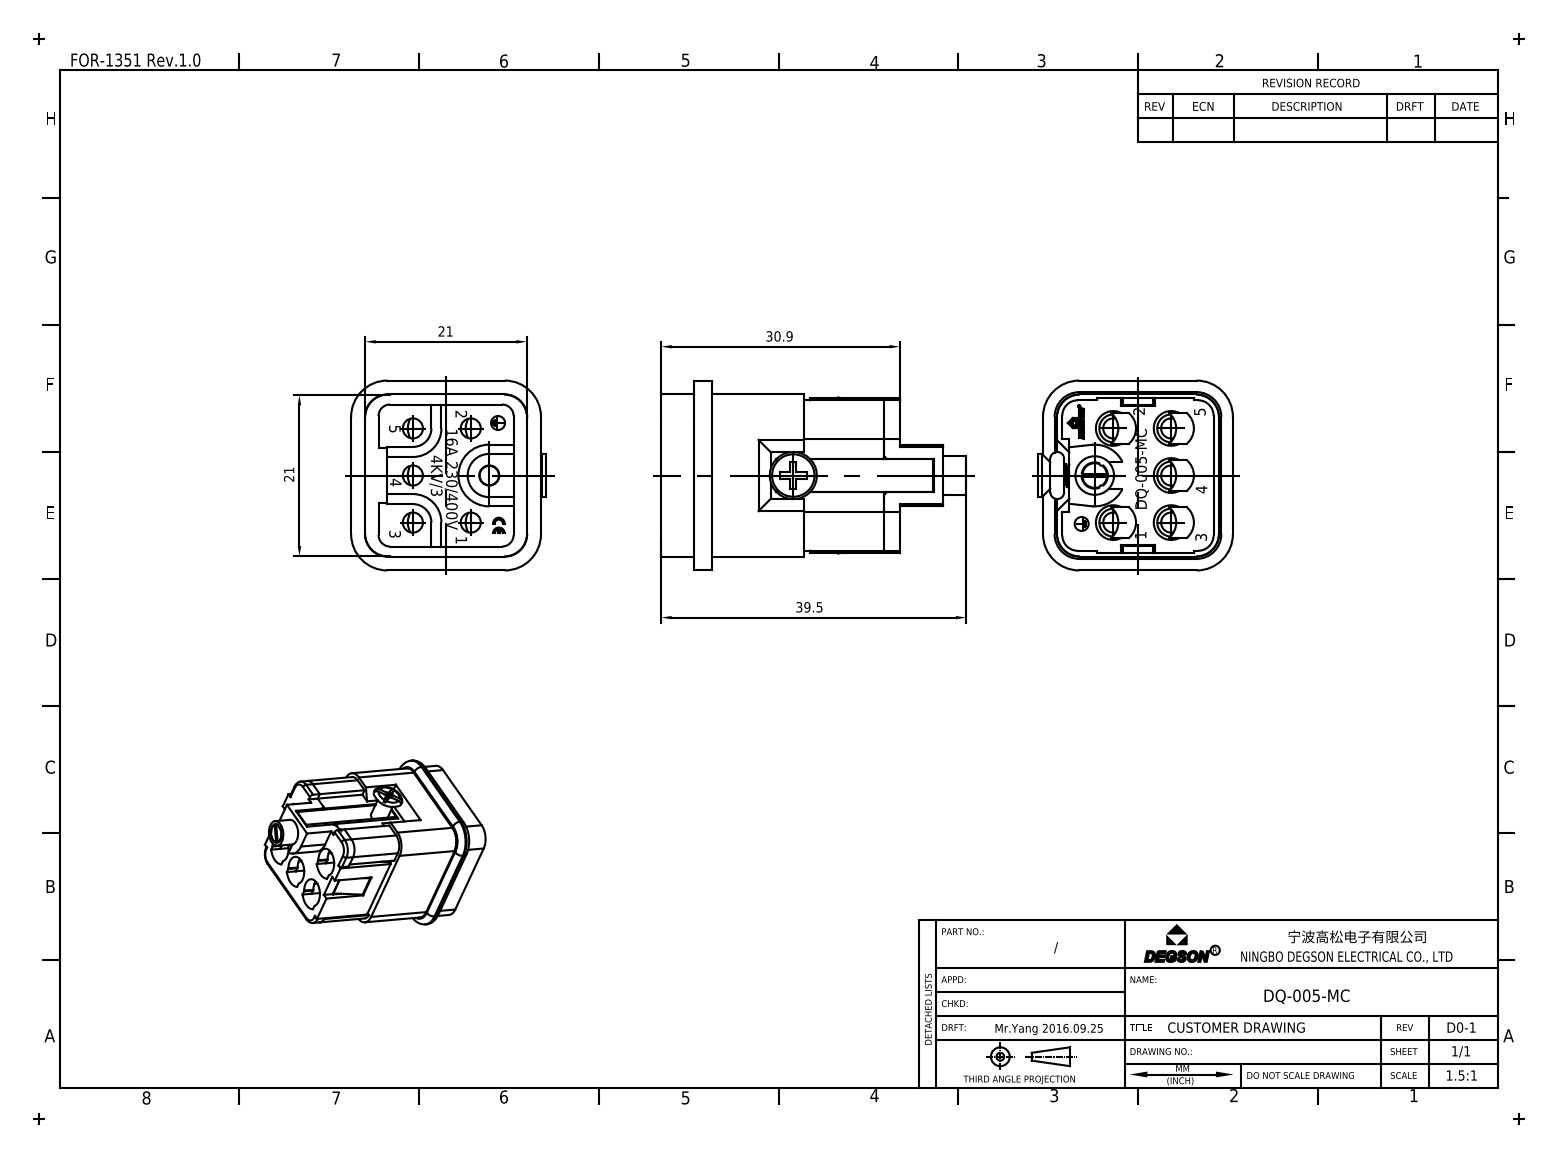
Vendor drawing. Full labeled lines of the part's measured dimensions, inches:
Part name (STEP PRODUCT): DQ-005-MC
STEP written by: CREO PARAMETRIC BY PTC INC, 2014350 (CONFIG_CONTROL_DESIGN)
Units: inches
Bodies: 1 solid, 256 faces (132 planar, 90 cylindrical, 34 other)
Overall size (bounding box): 1.559 × 0.945 × 0.945
Volume: 0.55 in³ · Surface area: 9.016 in²
Round holes (diameter × count): ⌀0.102 ×6, ⌀0.134 ×1, ⌀0.197 ×1
Round bosses / shafts (diameter × count): ⌀0.217 ×1, ⌀0.126 ×1, ⌀0.122 ×1, ⌀0.113 ×1, ⌀0.098 ×1
Partial cylindrical surfaces — rounded edges, fillets, slot ends (radius × count): R0.008 ×13, R0.118 ×11, R0.096 ×5, R0.02 ×4, R0.059 ×4, R0.079 ×4, R0.165 ×4, R0.01 ×2
Main face-to-face distances: 0.051, 0.776, 0.827, 0.717, 0.76, 0.03, 0.797, 0.067, 0.031, 0.73
Hole centre spacings: 0.24, 0.258, 0.295, 0.381, 0.458, 0.48, 0.564, 0.39
